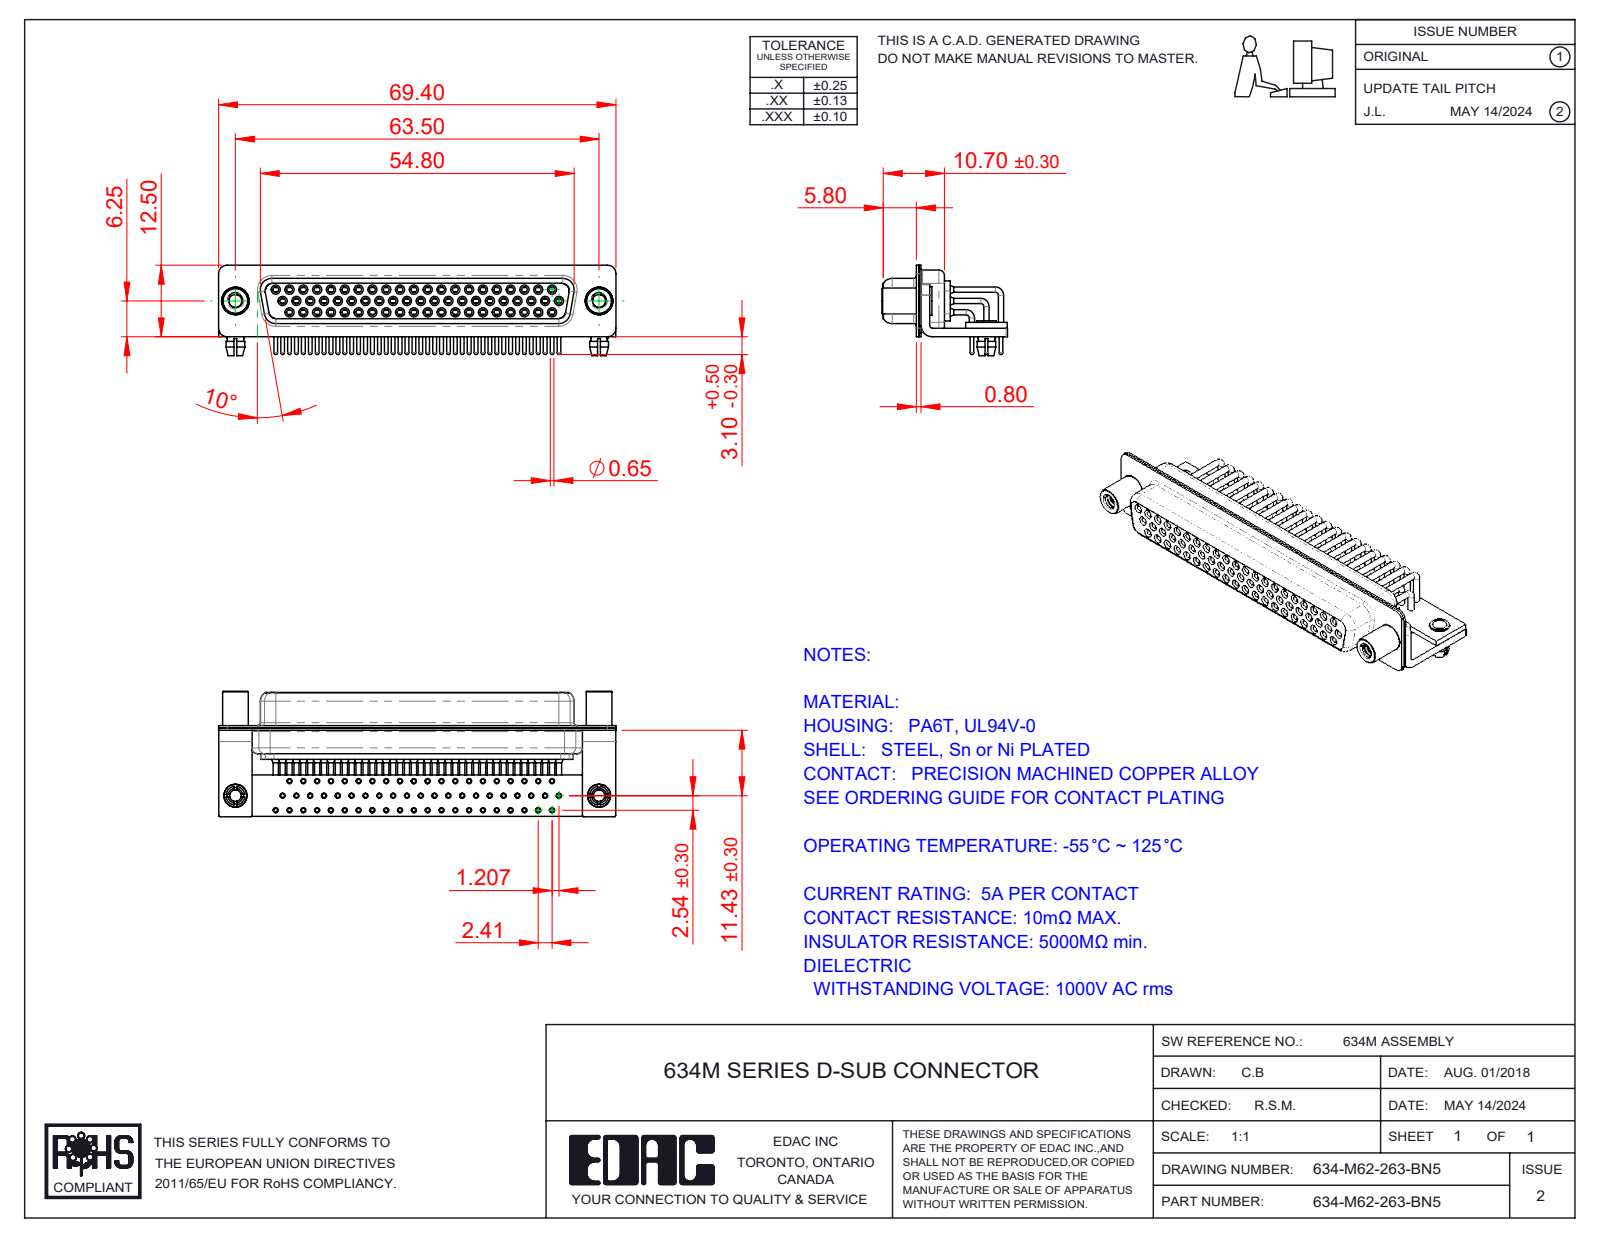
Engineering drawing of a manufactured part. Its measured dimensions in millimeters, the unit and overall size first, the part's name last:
Units: millimetres
Overall size (bounding box): 69.4 × 21.9 × 15.8
Round holes (diameter × count): ⌀2 ×64, ⌀0.9 ×62, ⌀1 ×62, ⌀1.1 ×62, ⌀1.7 ×62, ⌀1.8 ×62, ⌀2.26 ×2, ⌀2.5 ×2, ⌀3.2 ×2, ⌀4 ×2, ⌀4.8 ×2
Round bosses / shafts (diameter × count): ⌀0.9 ×118, ⌀1.6 ×62, ⌀1.5 ×62, ⌀0.65 ×62, ⌀2 ×56, ⌀5 ×2, ⌀4.9 ×2, ⌀4.5 ×2
Partial cylindrical surfaces — rounded edges, fillets, slot ends (radius × count): R0.25 ×16, R1.5 ×16, R2 ×13, R1.35 ×8, R1.6 ×8, R0.5 ×5, R0.6 ×4, R0.65 ×4
Main face-to-face distances: 0.4, 2.3, 1.9, 1, 8.5, 1.45, 8.95, 0.85, 0.8, 9.35
Hole centre spacings: 7.24, 2.41, 9.65, 4.83, 14.48, 16.89, 2.81, 2.32
Volume: 6 304 mm³ · Surface area: 20 284 mm²
Bodies: 72 solids, 3881 faces (1073 planar, 1783 cylindrical, 1025 other)
Part name (STEP PRODUCT): 634M Contact Row 3; 634M Stabilizer Bracket; 634M Shell Rear_62 Contacts; 634M Housing_62 Contacts (+7 more)
STEP written by: SolidWorks 2016 (CONFIG_CONTROL_DESIGN)
